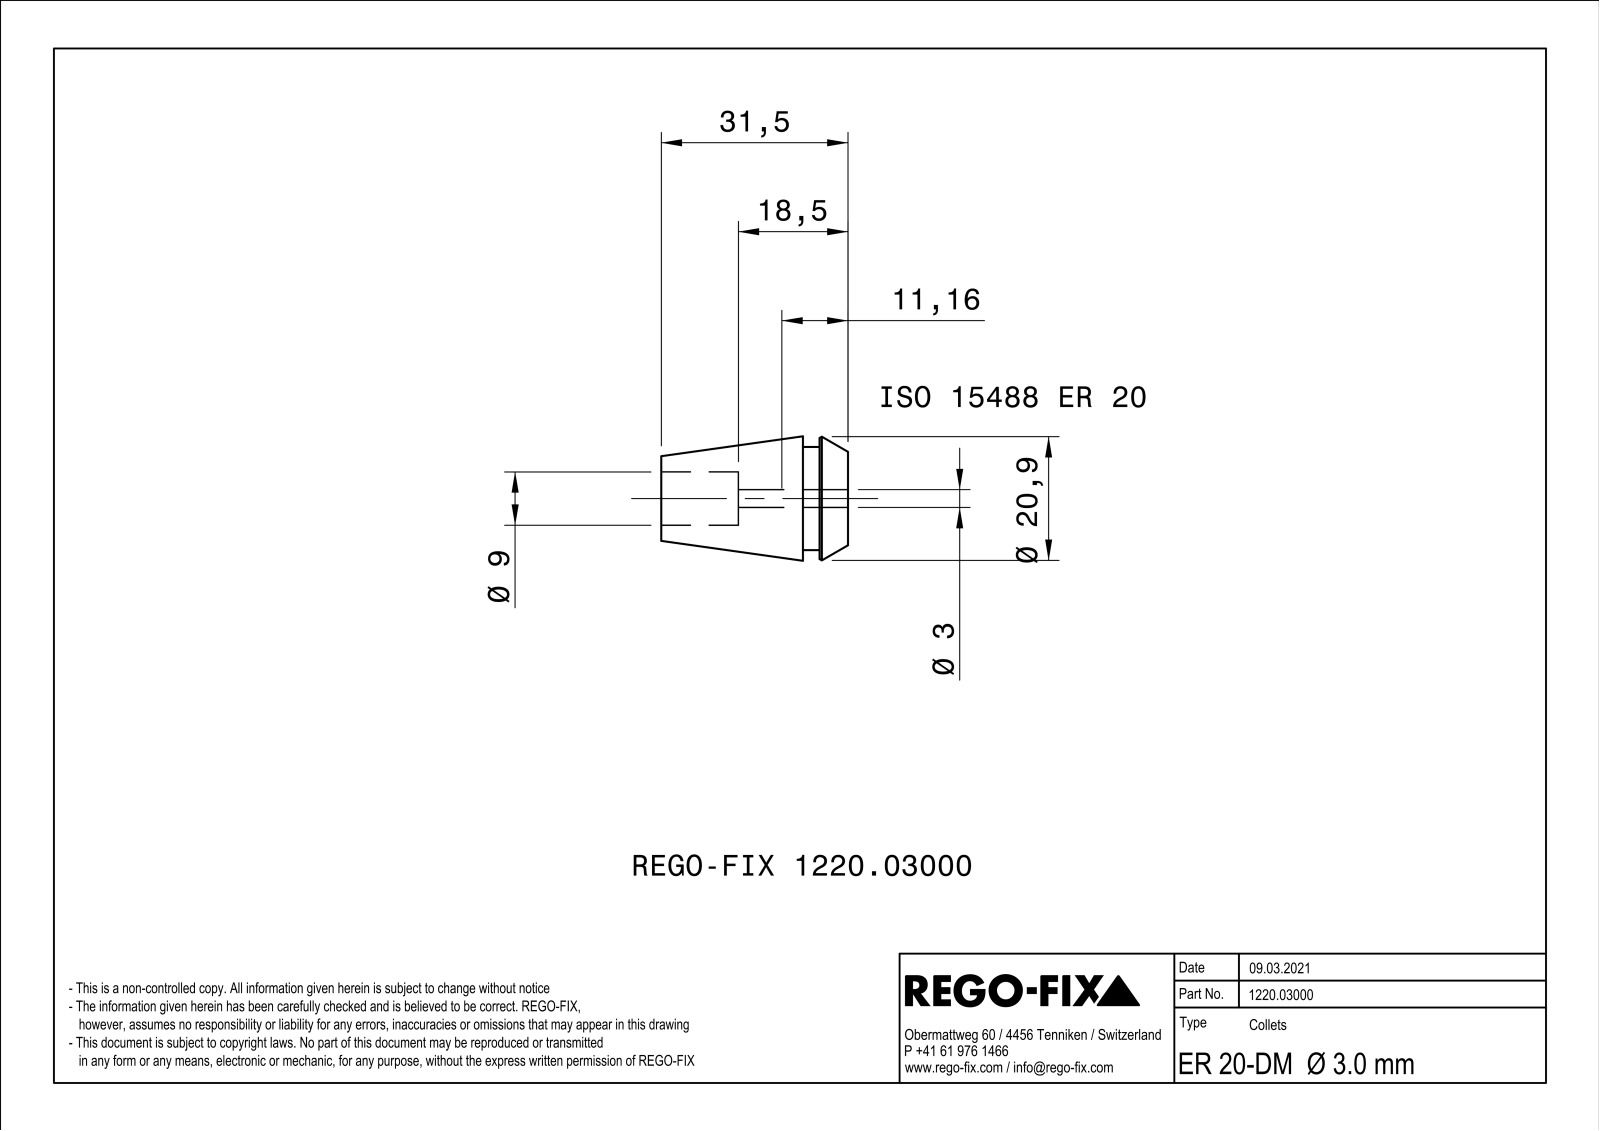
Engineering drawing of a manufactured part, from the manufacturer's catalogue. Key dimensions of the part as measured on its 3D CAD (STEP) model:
Part name (STEP PRODUCT): NOCUT
STEP written by: SIEMENS PLM Software Solid Edge ST10 (AUTOMOTIVE_DESIGN)
Units: millimetres
Bodies: 1 solid, 94 faces (44 planar, 9 cylindrical, 41 other)
Overall size (bounding box): 31.5 × 20.6 × 20.6
Volume: 5 806 mm³ · Surface area: 4 387 mm²
Round holes (diameter × count): ⌀3 ×1, ⌀9 ×1
Round bosses / shafts (diameter × count): ⌀17.4 ×1
Main face-to-face distances: 0.5, 7.6, 4.8, 2.8, 31.5, 26.7, 23.9, 18.5, 13.7, 10.9
